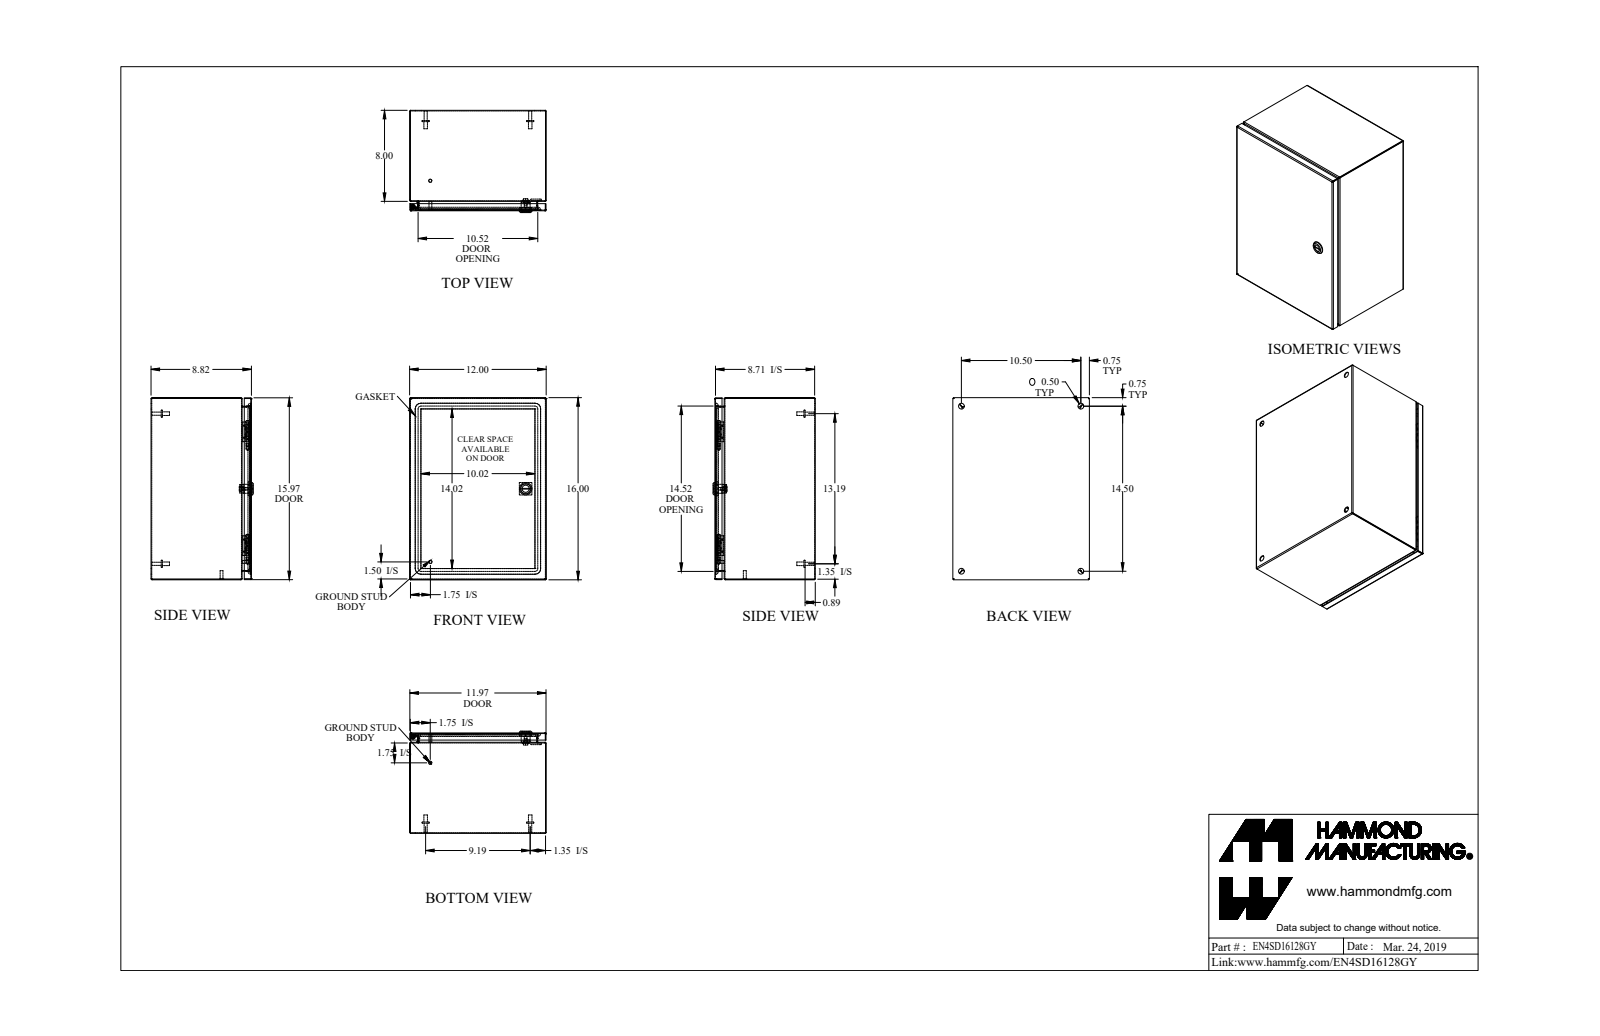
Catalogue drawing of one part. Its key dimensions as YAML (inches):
part_name: "EN4SD16128GY_Default"
step_written_by: "SolidWorks 2019 (CONFIG_CONTROL_DESIGN)"
units: inches
bodies: {solids: 21, faces: 634, planar: 285, cylindrical: 213, other: 136}
overall_size: [16, 12, 8.982]
volume: 59.35
surface_area: 2008
round_holes:
  - {diameter: 0.5, count: 4}
  - {diameter: 0.172, count: 1}
  - {diameter: 0.232, count: 1}
  - {diameter: 0.24, count: 1}
  - {diameter: 0.242, count: 1}
  - {diameter: 0.625, count: 1}
  - {diameter: 0.785, count: 1}
round_bosses_or_shafts:
  - {diameter: 0.625, count: 4}
  - {diameter: 0.313, count: 4}
  - {diameter: 0.27, count: 4}
  - {diameter: 0.281, count: 2}
  - {diameter: 0.25, count: 2}
  - {diameter: 1.1, count: 1}
  - {diameter: 0.525, count: 1}
  - {diameter: 0.455, count: 1}
partial_cylinders:
  - {radius: 0.029, count: 21}
  - {radius: 0.086, count: 21}
  - {radius: 0.25, count: 16}
  - {radius: 19, count: 8}
  - {radius: 0.006, count: 4}
  - {radius: 0.062, count: 4}
  - {radius: 0.499, count: 4}
  - {radius: 0.125, count: 2}
face_to_face_distances: [0.057, 8.765, 11.943, 8.708, 8.822, 15.943, 11.886, 12, 15.886, 16]
hole_center_spacings: [10.5, 14.5, 17.902, 7.326, 7.327, 11.903, 11.904]
